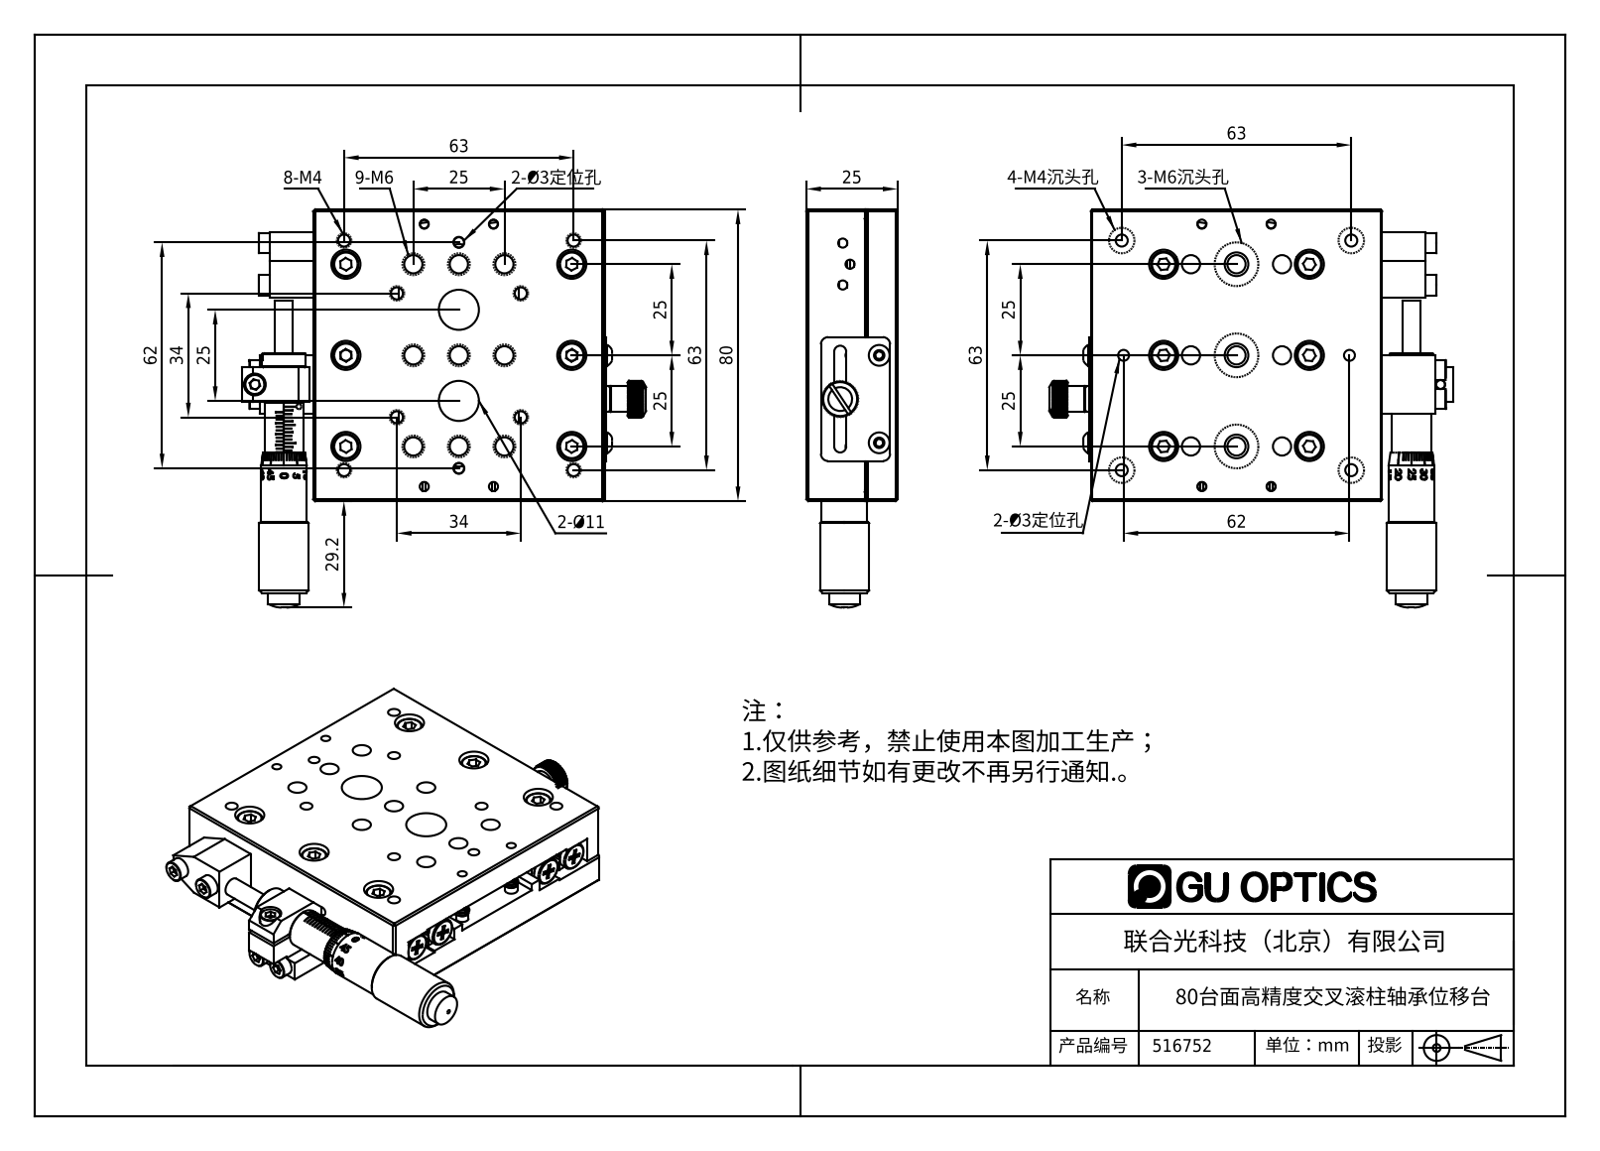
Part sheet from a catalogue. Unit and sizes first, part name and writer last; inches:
Units: inches
Overall size (bounding box): 4.366 × 4.299 × 0.984
Round holes (diameter × count): ⌀0.295 ×4
Round bosses / shafts (diameter × count): ⌀0.098 ×13, ⌀0.315 ×12, ⌀0.13 ×12, ⌀0.197 ×10, ⌀0.433 ×5, ⌀0.177 ×4, ⌀0.138 ×4, ⌀0.118 ×4
Partial cylindrical surfaces — rounded edges, fillets, slot ends (radius × count): R0.079 ×4, R0.065 ×2, R0.197 ×1, R0.21 ×1, R0.246 ×1
Main face-to-face distances: 0.315, 0.669, 0.984, 0.335, 0.02, 0.354, 0.079, 0.276, 0.039, 0.591
Hole centre spacings: 0.394, 2.008, 1.614, 2.402
Bodies: 0 solids, 1288 faces (688 planar, 301 cylindrical, 299 other)
Part name (STEP PRODUCT): 80台面高精度交叉滚柱轴承位移台
STEP written by: SolidWorks 2016 (AUTOMOTIVE_DESIGN)
